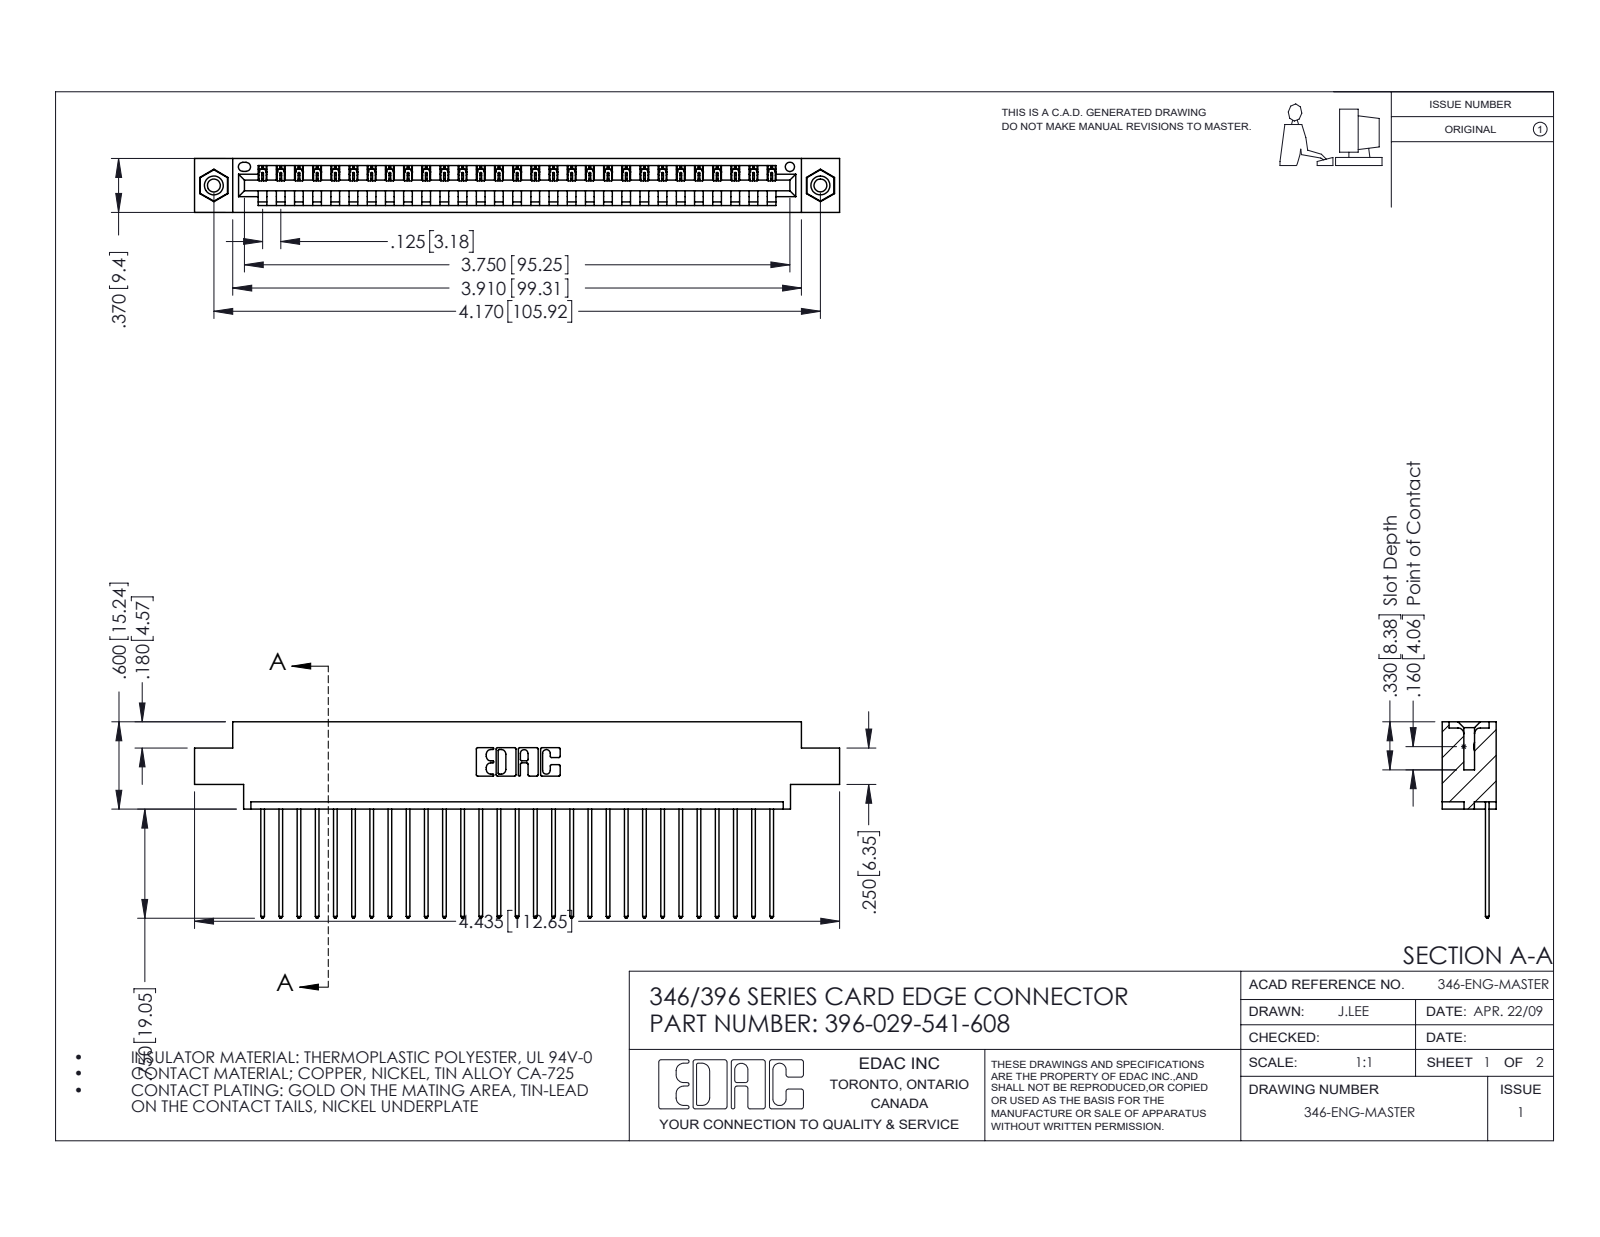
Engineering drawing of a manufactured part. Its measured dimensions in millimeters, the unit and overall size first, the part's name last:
Units: millimetres
Overall size (bounding box): 112.6 × 34.3 × 9.4
Round holes (diameter × count): ⌀2.3 ×2, ⌀3.2 ×2, ⌀4 ×2, ⌀1.6 ×1
Round bosses / shafts (diameter × count): ⌀3.9 ×2
Partial cylindrical surfaces — rounded edges, fillets, slot ends (radius × count): R0.2 ×58, R0.3 ×58, R0.3 ×22, R0.2 ×6, R0.8 ×6, R0.7 ×3, R0.8 ×2, R1 ×2
Main face-to-face distances: 1.2, 8.2, 9.4, 6.4, 1.8, 7.6, 0.6, 5.6, 3.8, 2.5
Hole centre spacings: 6.2, 100.6, 105.9
Volume: 10 600 mm³ · Surface area: 13 900 mm²
Bodies: 32 solids, 1868 faces (1272 planar, 580 cylindrical, 16 other)
Part name (STEP PRODUCT): 345-250-001_345-250-003-102; 396-029-541-608; 346 Part_0.170 Offset - 0.156 Dia-TI; 345-292-001_345-293-141
STEP written by: SolidWorks 2016 (CONFIG_CONTROL_DESIGN)
